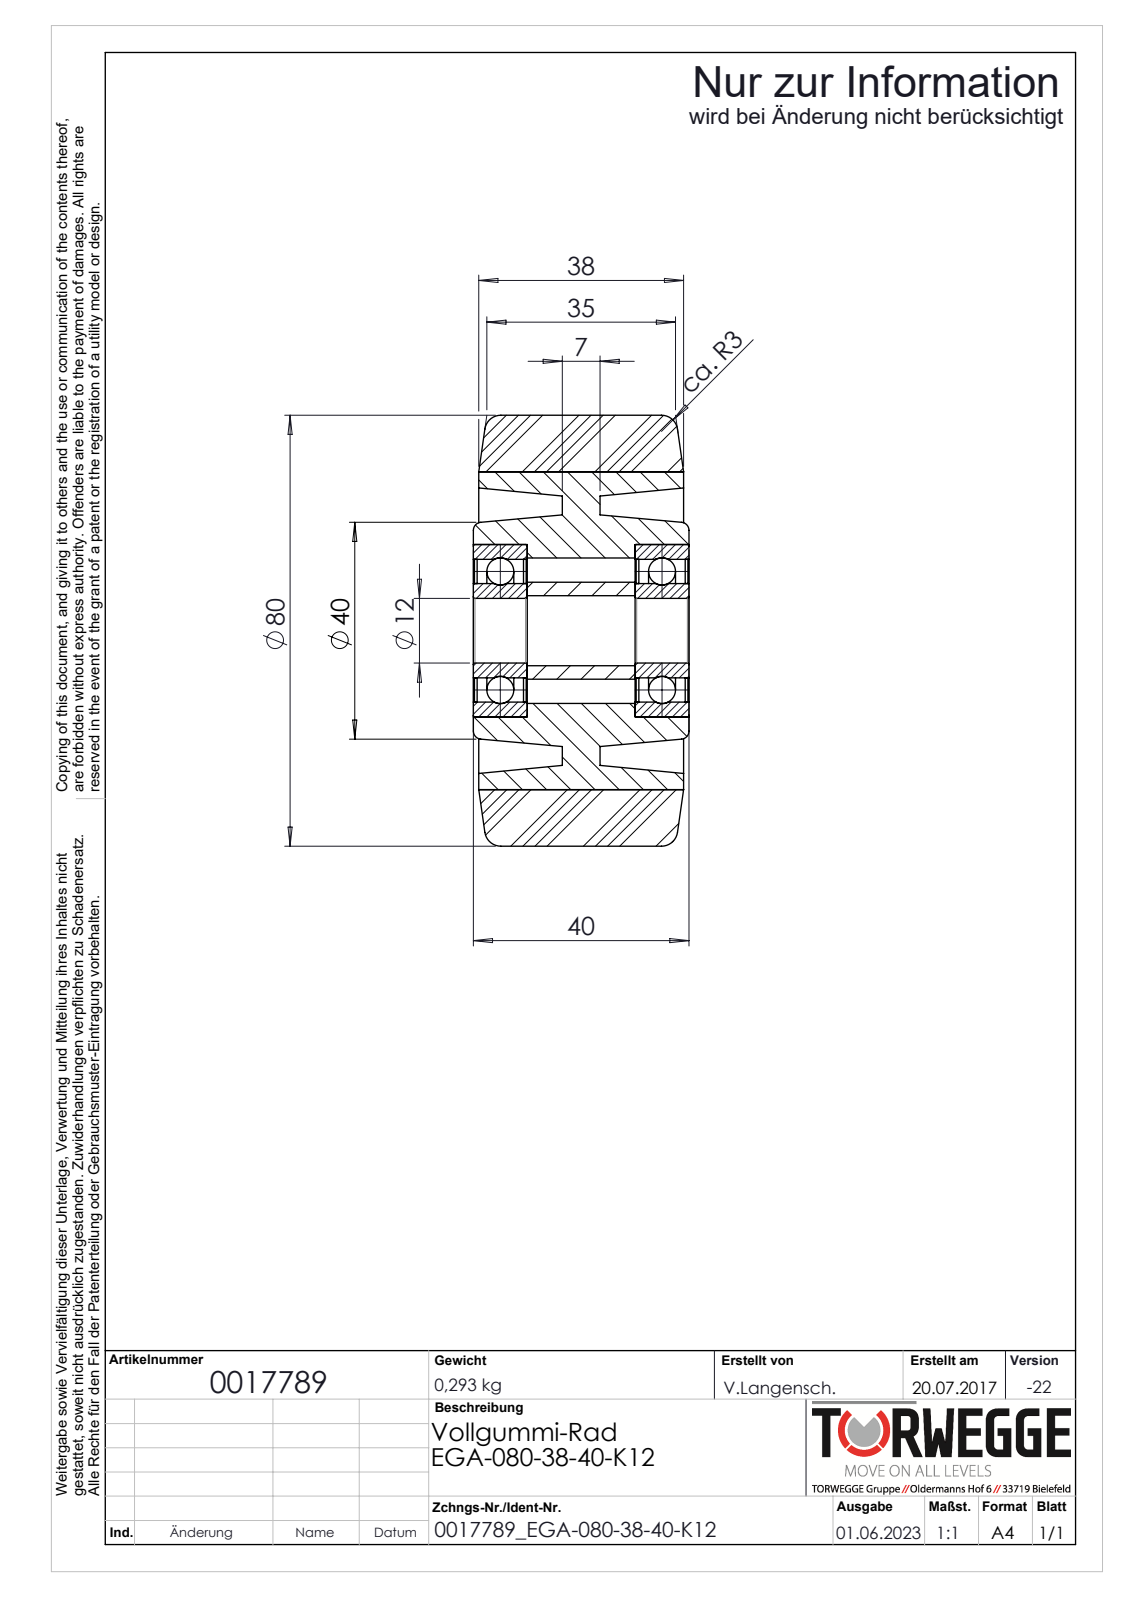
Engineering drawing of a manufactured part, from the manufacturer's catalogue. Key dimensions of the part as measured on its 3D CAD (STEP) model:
Part name (STEP PRODUCT): 0017789
STEP written by: SolidWorks 2018 (AUTOMOTIVE_DESIGN)
Units: millimetres
Bodies: 13 solids, 138 faces (26 planar, 56 cylindrical, 56 other)
Overall size (bounding box): 80 × 80 × 40
Volume: 152 387 mm³ · Surface area: 57 570 mm²
Round holes (diameter × count): ⌀12 ×1, ⌀13 ×1, ⌀17.5 ×1, ⌀26.5 ×1, ⌀27 ×1, ⌀32 ×1, ⌀59 ×1
Round bosses / shafts (diameter × count): ⌀80 ×1, ⌀18 ×1
Main face-to-face distances: 30, 0.7, 9.3, 9.8, 0.5, 9.1, 10, 1, 39, 9
